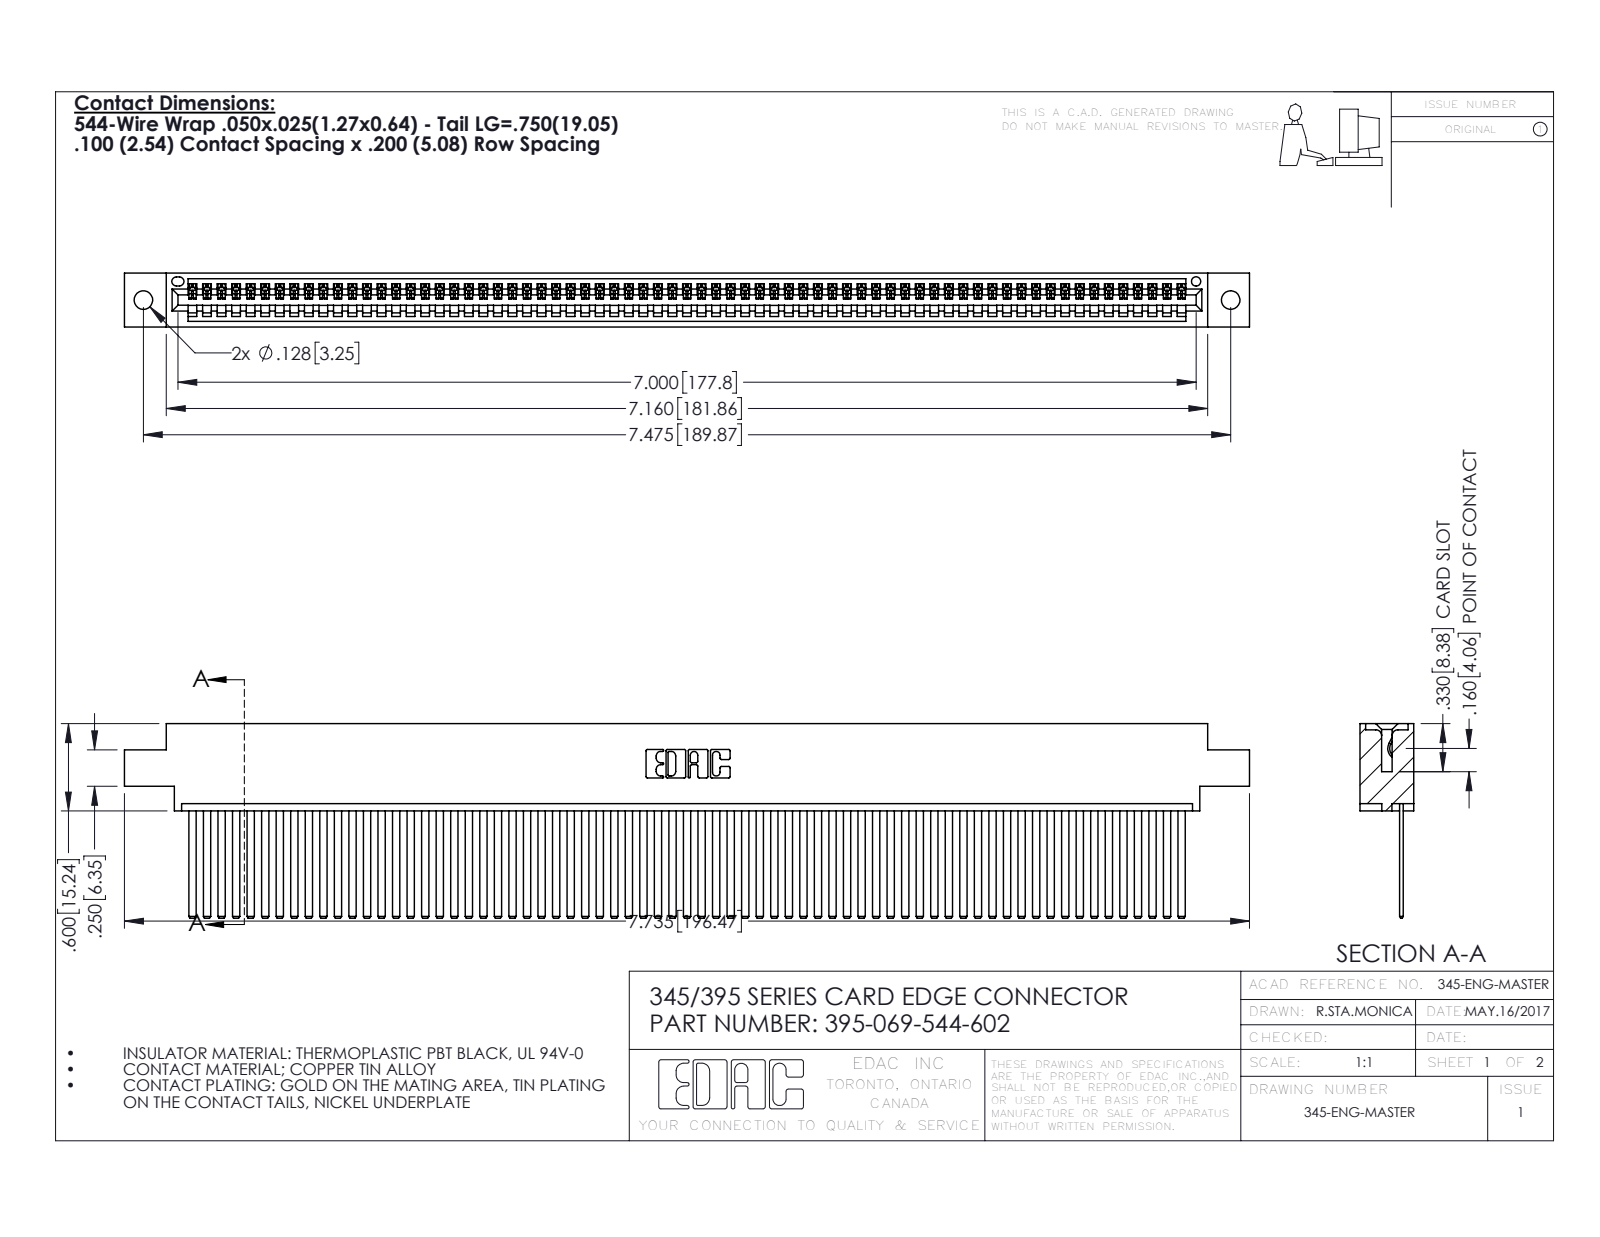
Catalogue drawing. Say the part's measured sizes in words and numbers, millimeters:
The part is named "345-292-001_345-293-144; 395-069-544-602; 345 Part_0.170 Offset - 0.128 Dia". Its 3-D file was written by "SolidWorks 2016 (CONFIG_CONTROL_DESIGN)". It is 70 solids with 3718 faces: 2568 planar, 1150 cylindrical and 0 other. Overall it measures 196.5 by 34 by 9.4 millimeters. Its volume is 19 530 cubic millimeters and its surface area 28 570 square millimeters. Round holes: 2 of diameter 3.3, 1 of diameter 1.6. Partial cylindrical surfaces (rounded edges, fillets, slot ends): 138 of radius 0.2, 22 of radius 0.3, 6 of radius 0.2, 6 of radius 0.8, 3 of radius 0.7, 2 of radius 0.8, 2 of radius 1, 1 of radius 0.4. The main face-to-face distances are 1.8, 7.6, 0.6, 2.5, 6.9, 9.4, 5.1, 5.7, 4.4, 3.8. The hole center spacings are 6.9, 183.9, 189.9.
